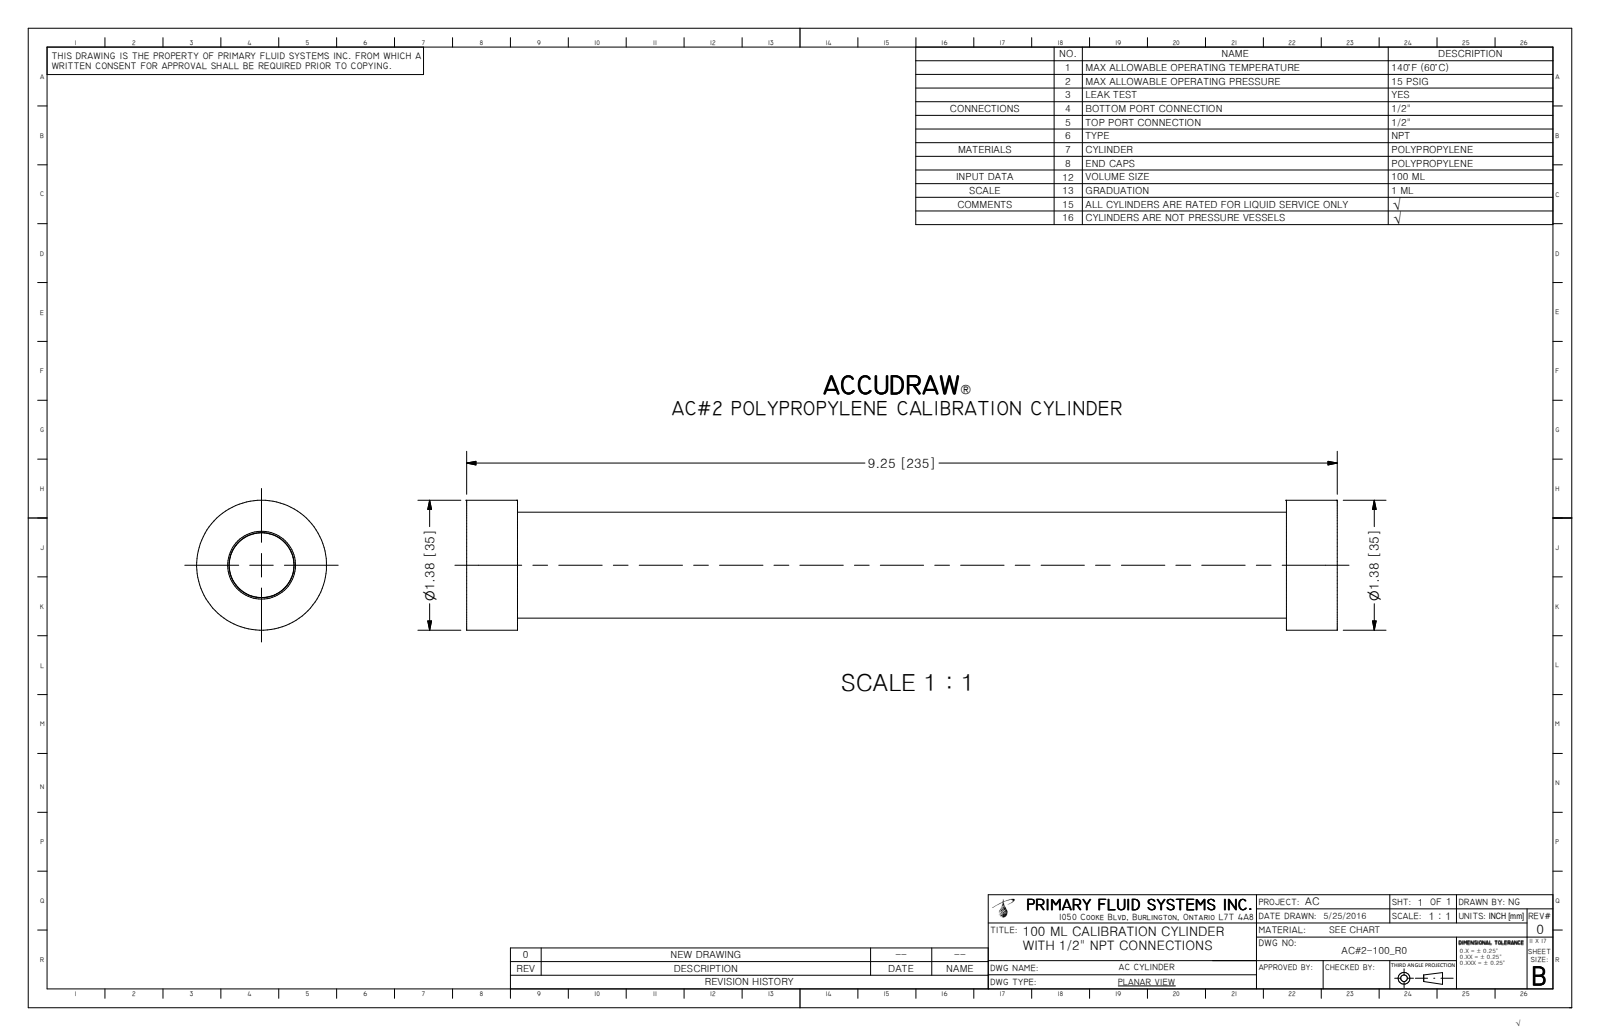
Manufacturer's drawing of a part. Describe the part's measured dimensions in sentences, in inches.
The part is named "AC#2-100_R0; AC-2B-100; AC-100-TUBE; AC-2T-100". Its 3-D file was written by "Autodesk Inventor 2009 (AUTOMOTIVE_DESIGN)". It is 3 solids with 20 faces: 8 planar, 6 cylindrical and 6 other. Overall it measures 9.25 by 1.38 by 1.38 inches. Its volume is 3.042 cubic inches and its surface area 68.86 square inches. Round holes: 1 of diameter 1.005. Round bosses or shafts: 1 of diameter 1.38, 1 of diameter 1.125, 1 of diameter 1.085, 1 of diameter 1.01. The main face-to-face distances are 0.54, 8.71, 9.25, 0.75, 8.5, 0.21, 7.96, 8.17, 7.75.
